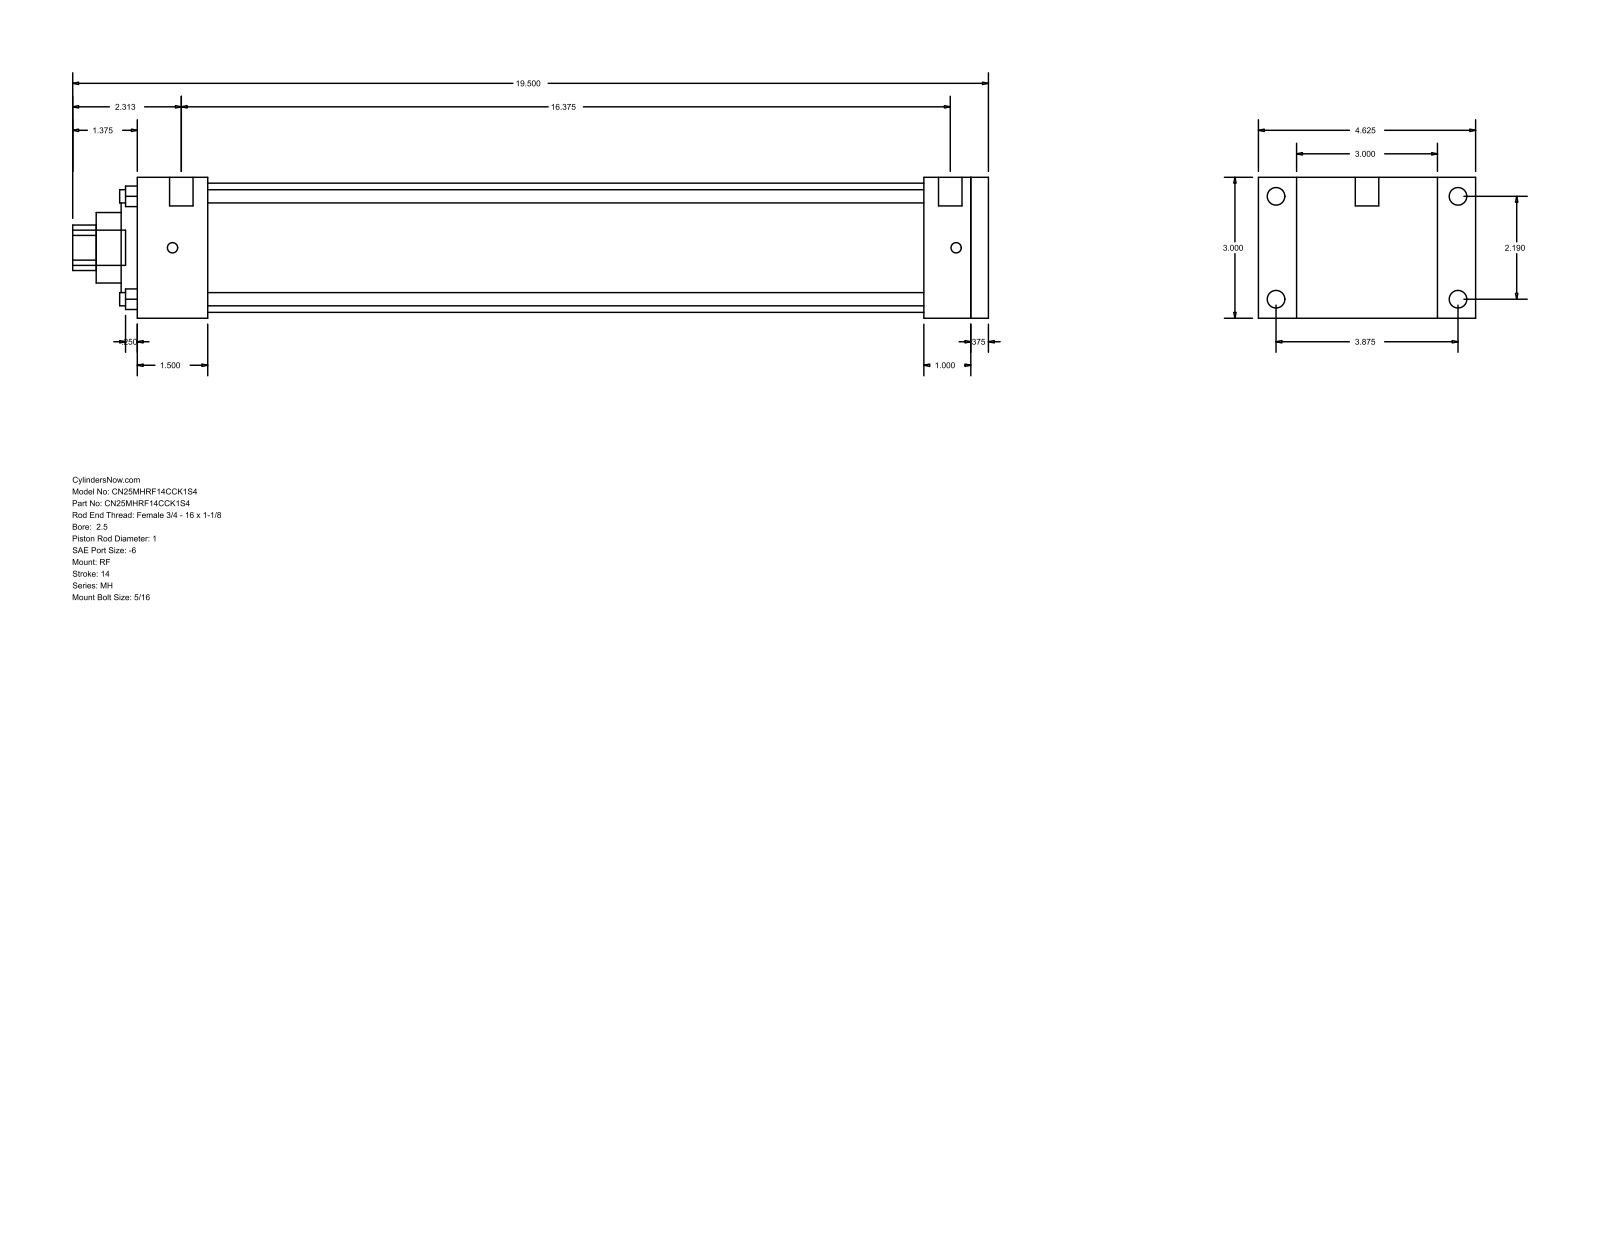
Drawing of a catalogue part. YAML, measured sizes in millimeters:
part_name: "MH_RF__0250_1"
step_written_by: "GSSL Pune (CONFIG_CONTROL_DESIGN)"
units: millimeters
bodies: {solids: 0, faces: 94, planar: 65, cylindrical: 29, other: 0}
overall_size: [495.3, 117.47, 76.2]
round_holes:
  - {diameter: 7.14, count: 4}
  - {diameter: 25.4, count: 1}
  - {diameter: 38.1, count: 1}
  - {diameter: 60.33, count: 1}
  - {diameter: 69.85, count: 1}
round_bosses_or_shafts:
  - {diameter: 9.53, count: 4}
  - {diameter: 5.56, count: 4}
  - {diameter: 12.7, count: 2}
  - {diameter: 19.05, count: 1}
partial_cylinders:
  - {radius: 12.29, count: 1}
face_to_face_distances: [76.2, 9.53, 460.38, 450.85, 34.92, 25.39, 425.46, 38.11, 387.35, 412.74]
hole_center_spacings: [39.33, 55.62, 78.66]
